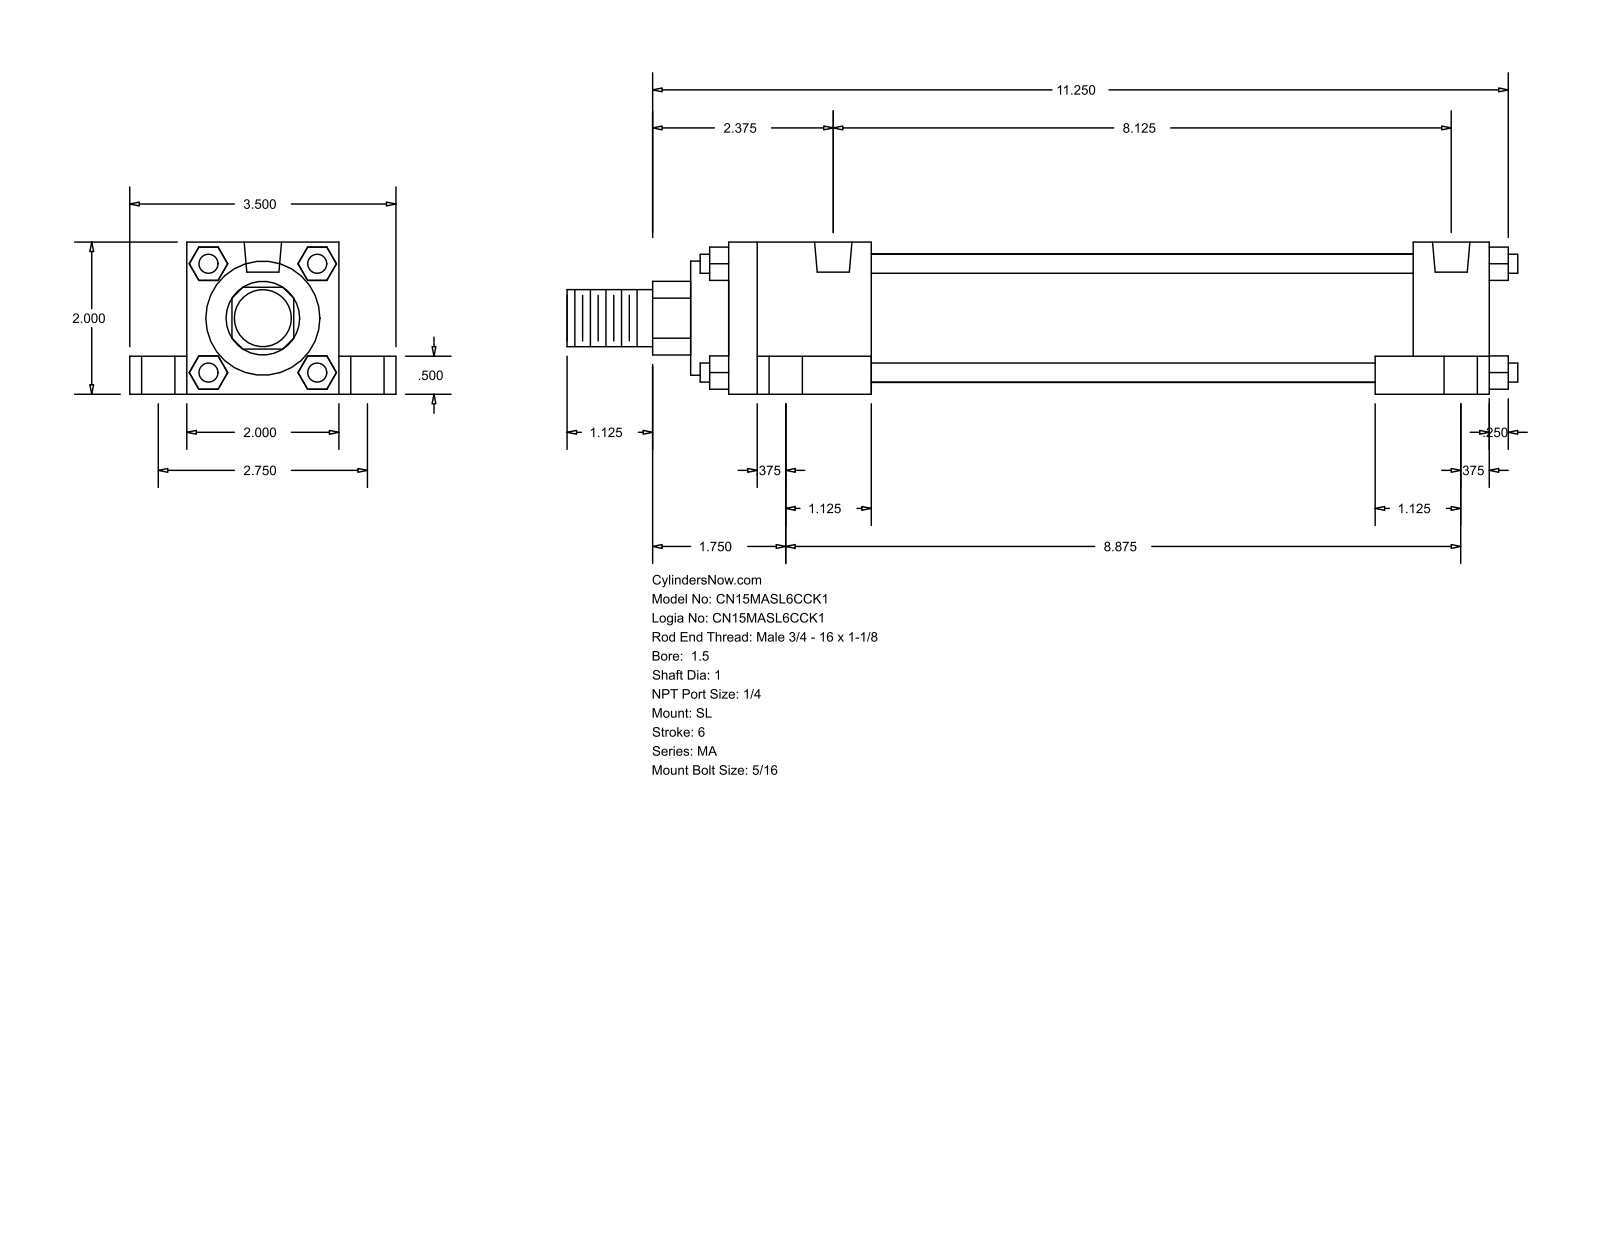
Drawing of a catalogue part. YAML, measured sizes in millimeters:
part_name: "MA_SL__0150_1"
step_written_by: "GSSL Pune (CONFIG_CONTROL_DESIGN)"
units: millimeters
bodies: {solids: 0, faces: 148, planar: 112, cylindrical: 36, other: 0}
overall_size: [317.5, 88.9, 50.8]
round_holes:
  - {diameter: 7.94, count: 4}
  - {diameter: 11.11, count: 4}
  - {diameter: 17.46, count: 4}
  - {diameter: 12.49, count: 2}
round_bosses_or_shafts:
  - {diameter: 6.35, count: 4}
  - {diameter: 42.93, count: 1}
  - {diameter: 38.1, count: 1}
  - {diameter: 25.4, count: 1}
  - {diameter: 19.05, count: 1}
partial_cylinders:
  - {radius: 12.29, count: 1}
face_to_face_distances: [50.8, 12.7, 19.05, 69.85, 38.1, 9.52, 254, 25.4, 6.35, 228.6]
hole_center_spacings: [35.06, 38.36, 69.84, 206.37, 212.44, 224.98, 225.43, 236]
